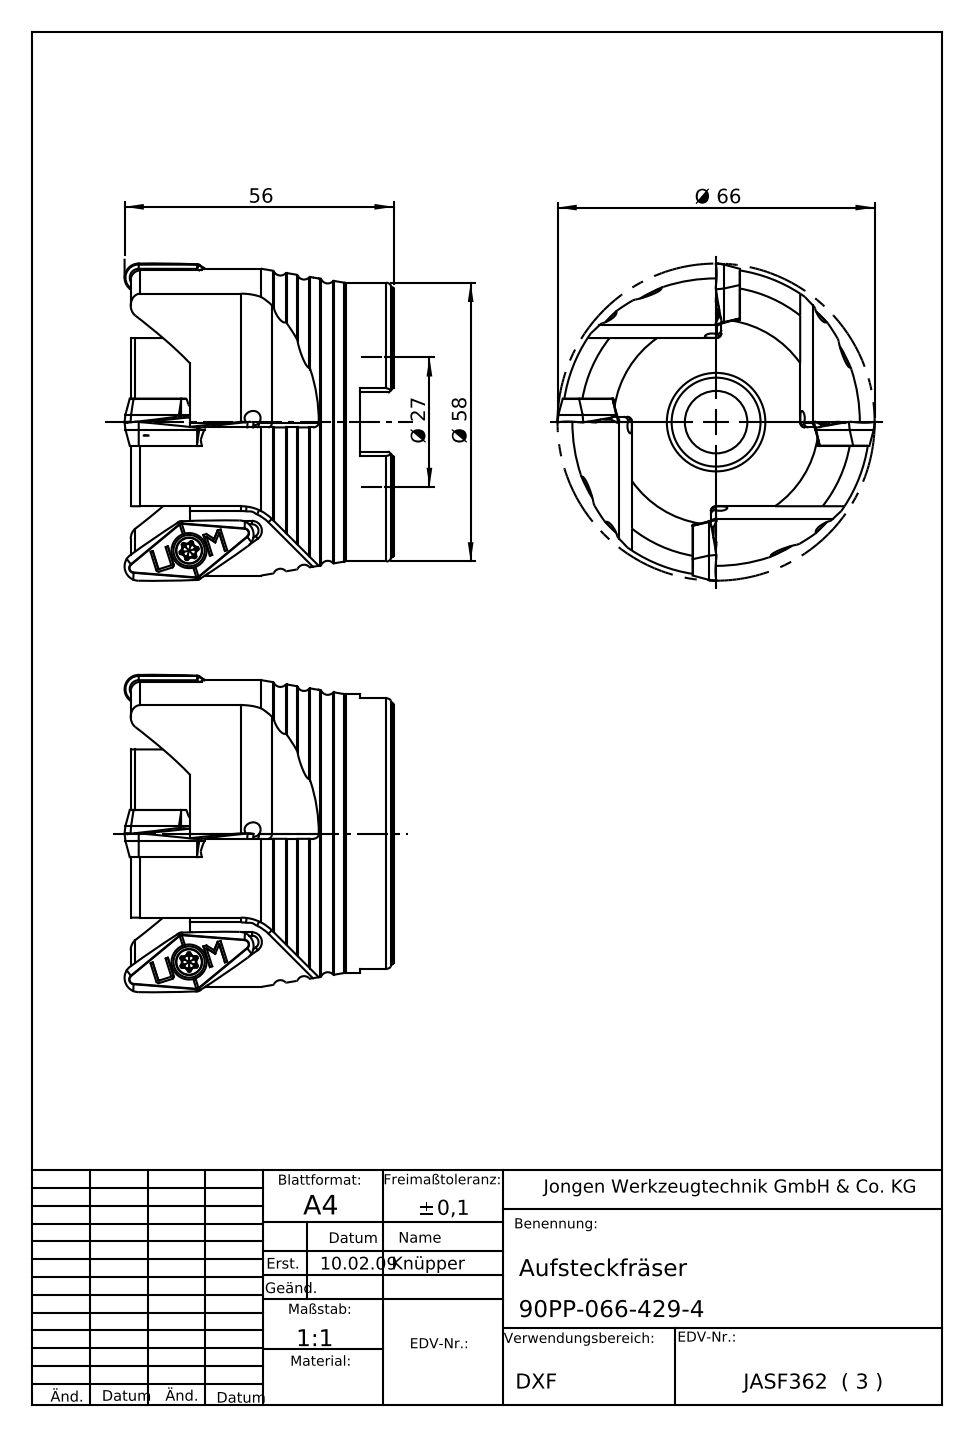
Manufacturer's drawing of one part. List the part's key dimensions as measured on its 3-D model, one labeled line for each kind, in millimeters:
Part name (STEP PRODUCT): 90PP-066-429-4
STEP written by: SolidWorks 2013 (AUTOMOTIVE_DESIGN)
Units: millimetres
Bodies: 1 solid, 156 faces (59 planar, 30 cylindrical, 67 other)
Overall size (bounding box): 66.06 × 66.06 × 56
Volume: 111 131 mm³ · Surface area: 23 554 mm²
Round holes (diameter × count): ⌀3 ×4, ⌀13 ×1, ⌀18.5 ×1, ⌀26.85 ×1, ⌀27.15 ×1, ⌀27.3 ×1
Round bosses / shafts (diameter × count): ⌀58 ×1
Partial cylindrical surfaces — rounded edges, fillets, slot ends (radius × count): R1 ×8, R1.36 ×4, R9 ×4, R31.95 ×1
Main face-to-face distances: 42.42, 16.4, 18.6, 35.42, 7, 17.42, 18, 25, 5.1, 7.3
